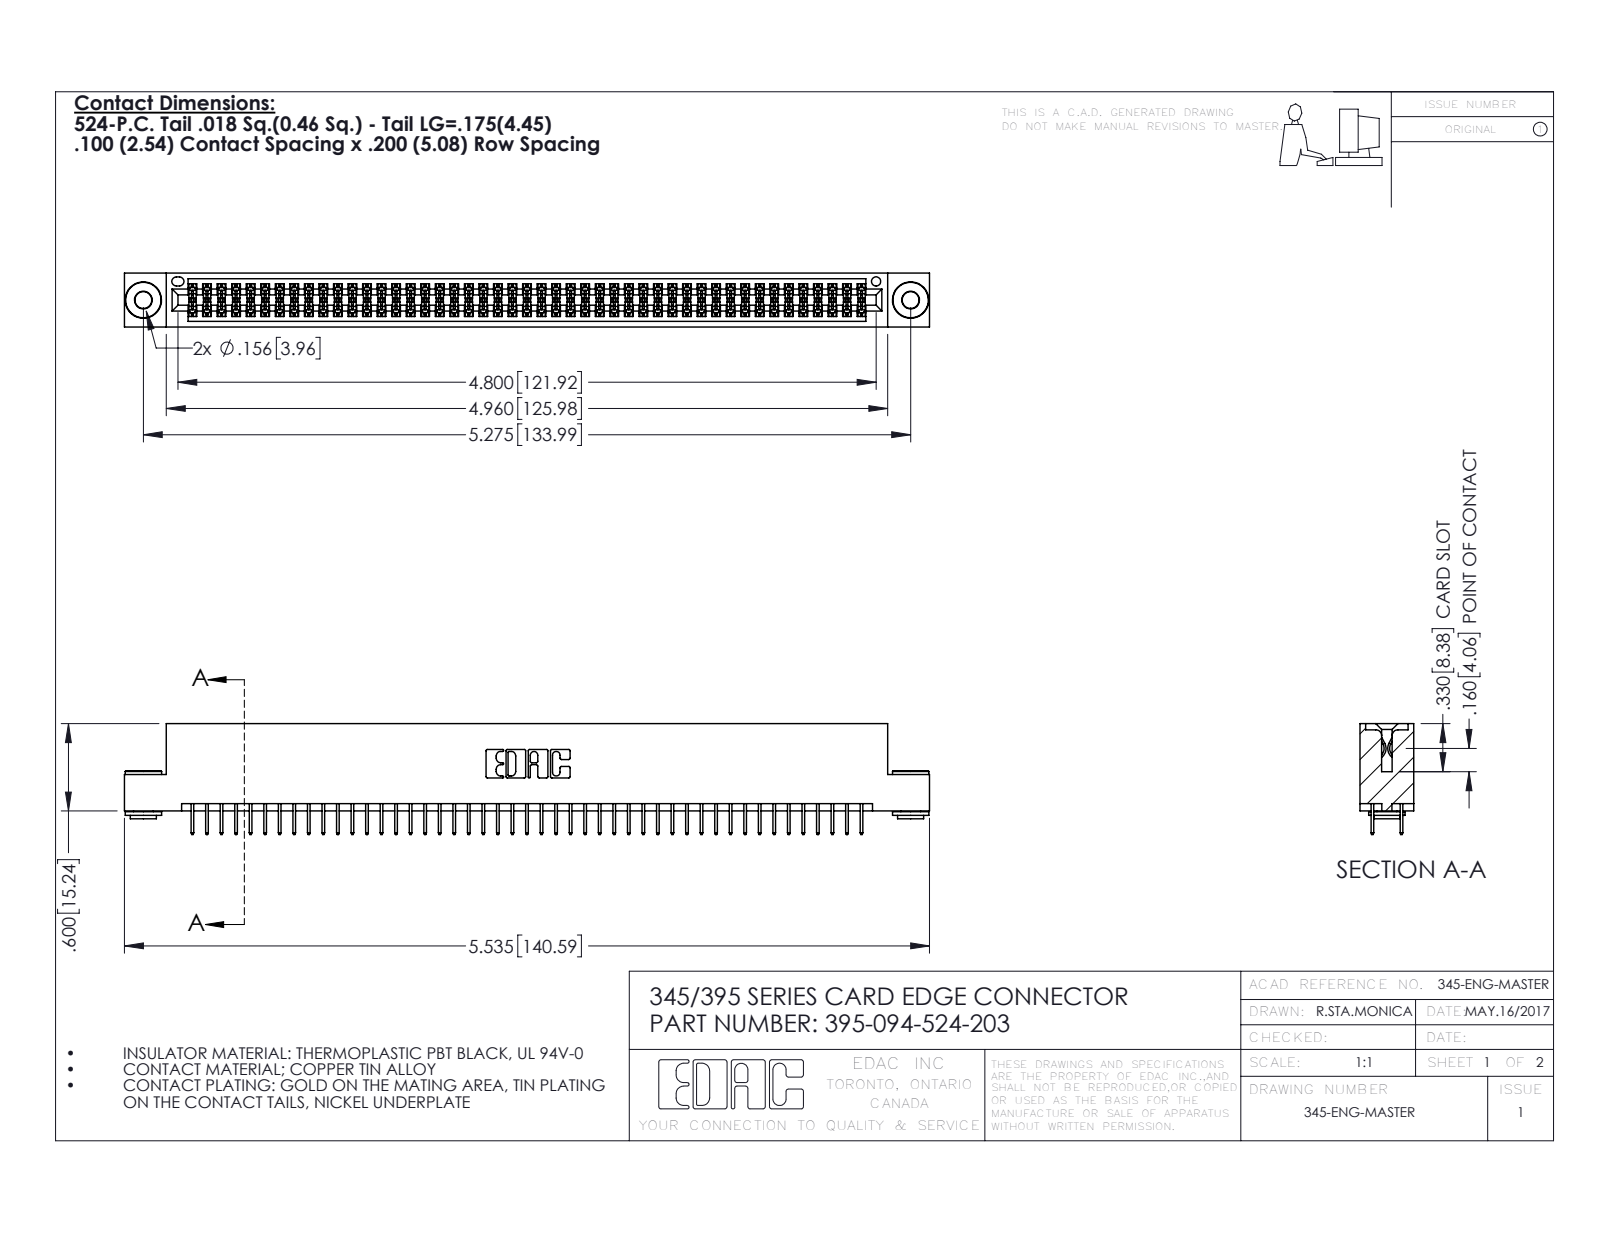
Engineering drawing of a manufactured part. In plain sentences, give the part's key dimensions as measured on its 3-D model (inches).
The part is named "345 Part_Flush Mounting Lugs - 0.156 Dia-TH; 345-292-001_345-293-124; 345-250-002_345-250-002-102; 395-094-524-203". Its 3-D file was written by "SolidWorks 2016 (CONFIG_CONTROL_DESIGN)". It is 97 solids with 5240 faces: 3756 planar, 1476 cylindrical and 8 other. Overall it measures 5.535 by 0.762 by 0.37 inches. Its volume is 0.829 cubic inches and its surface area 31 square inches. Round holes: 2 of diameter 0.116, 2 of diameter 0.156, 1 of diameter 0.064. Round bosses or shafts: 2 of diameter 0.25, 2 of diameter 0.18, 2 of diameter 0.136. Partial cylindrical surfaces (rounded edges, fillets, slot ends): 141 of radius 0.006, 22 of radius 0.01, 6 of radius 0.007, 6 of radius 0.031, 3 of radius 0.026, 2 of radius 0.014, 2 of radius 0.019, 2 of radius 0.022. The main face-to-face distances are 0.072, 0.298, 0.2, 0.37, 0.025, 0.098, 0.272, 0.225, 0.072, 0.175. The hole center spacings are 0.27, 5.039, 5.275.
